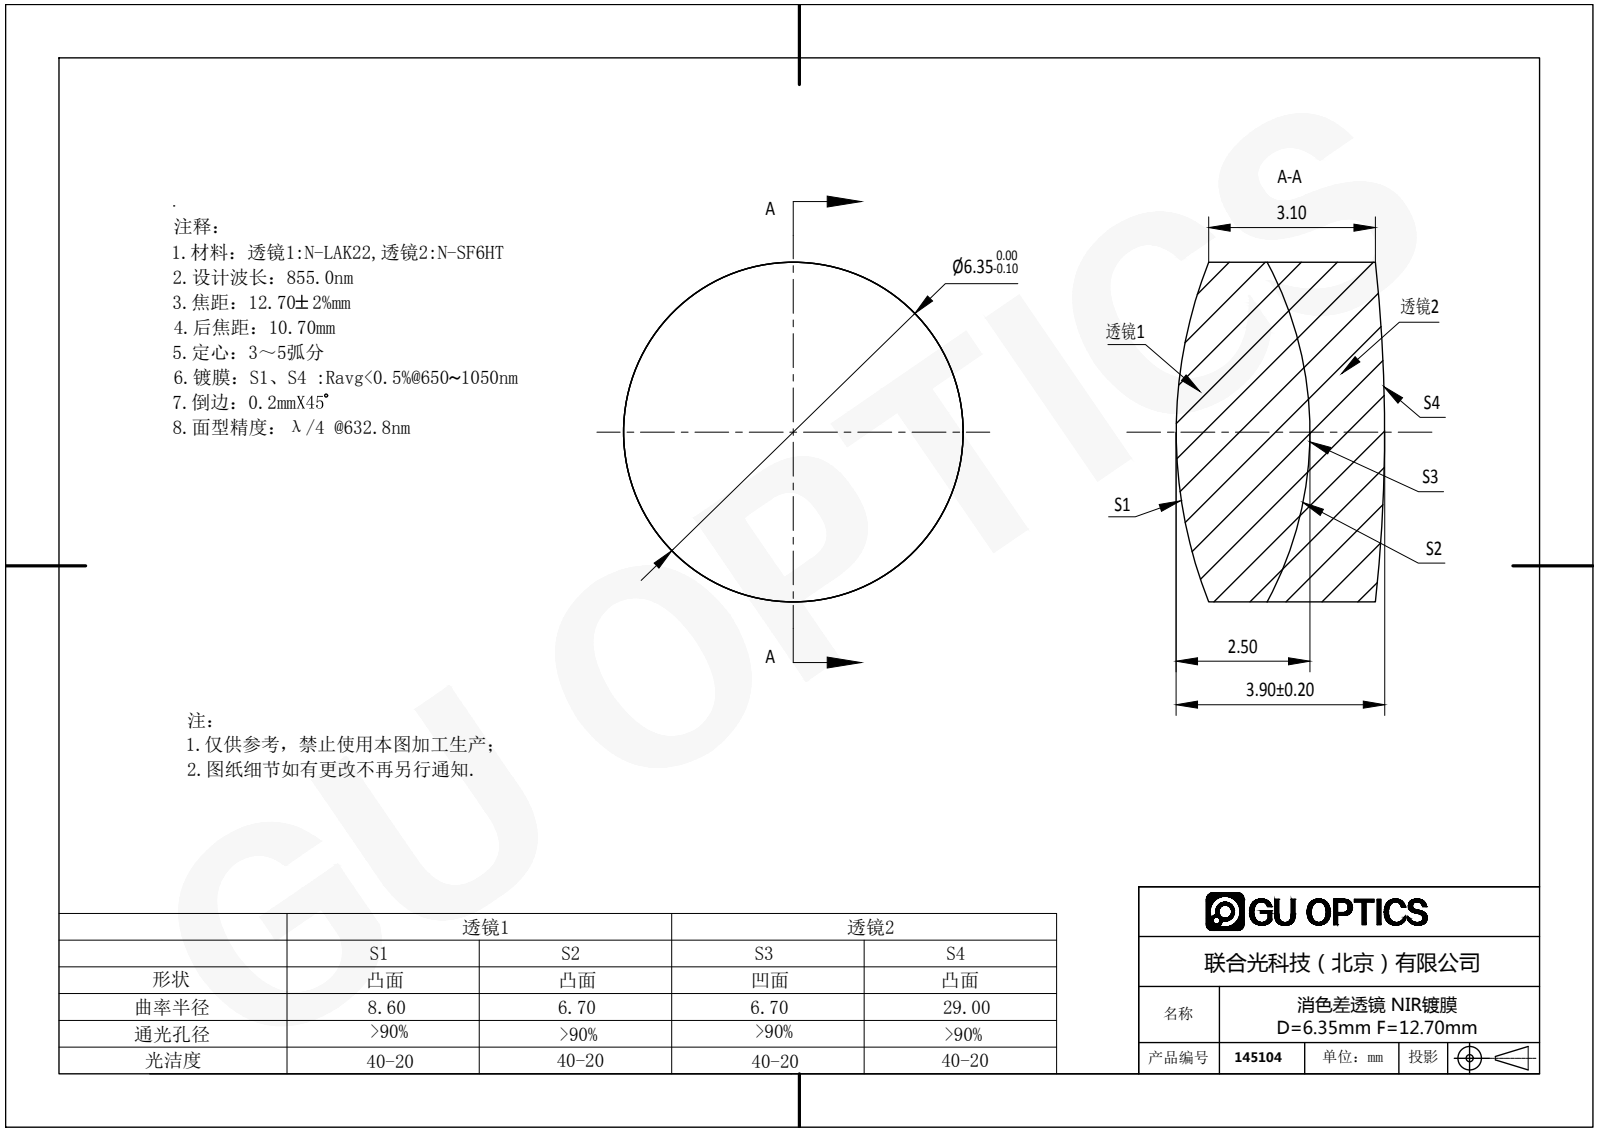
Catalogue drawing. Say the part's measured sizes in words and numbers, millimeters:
The part is named "145104". Its 3-D file was written by "SolidWorks 2016 (AUTOMOTIVE_DESIGN)". It is 2 solids with 12 faces: 0 planar, 4 cylindrical and 8 other. Overall it measures 6.35 by 6.35 by 3.9 millimeters. Its volume is 111 cubic millimeters and its surface area 194 square millimeters. Round bosses or shafts: 1 of diameter 6.35.
